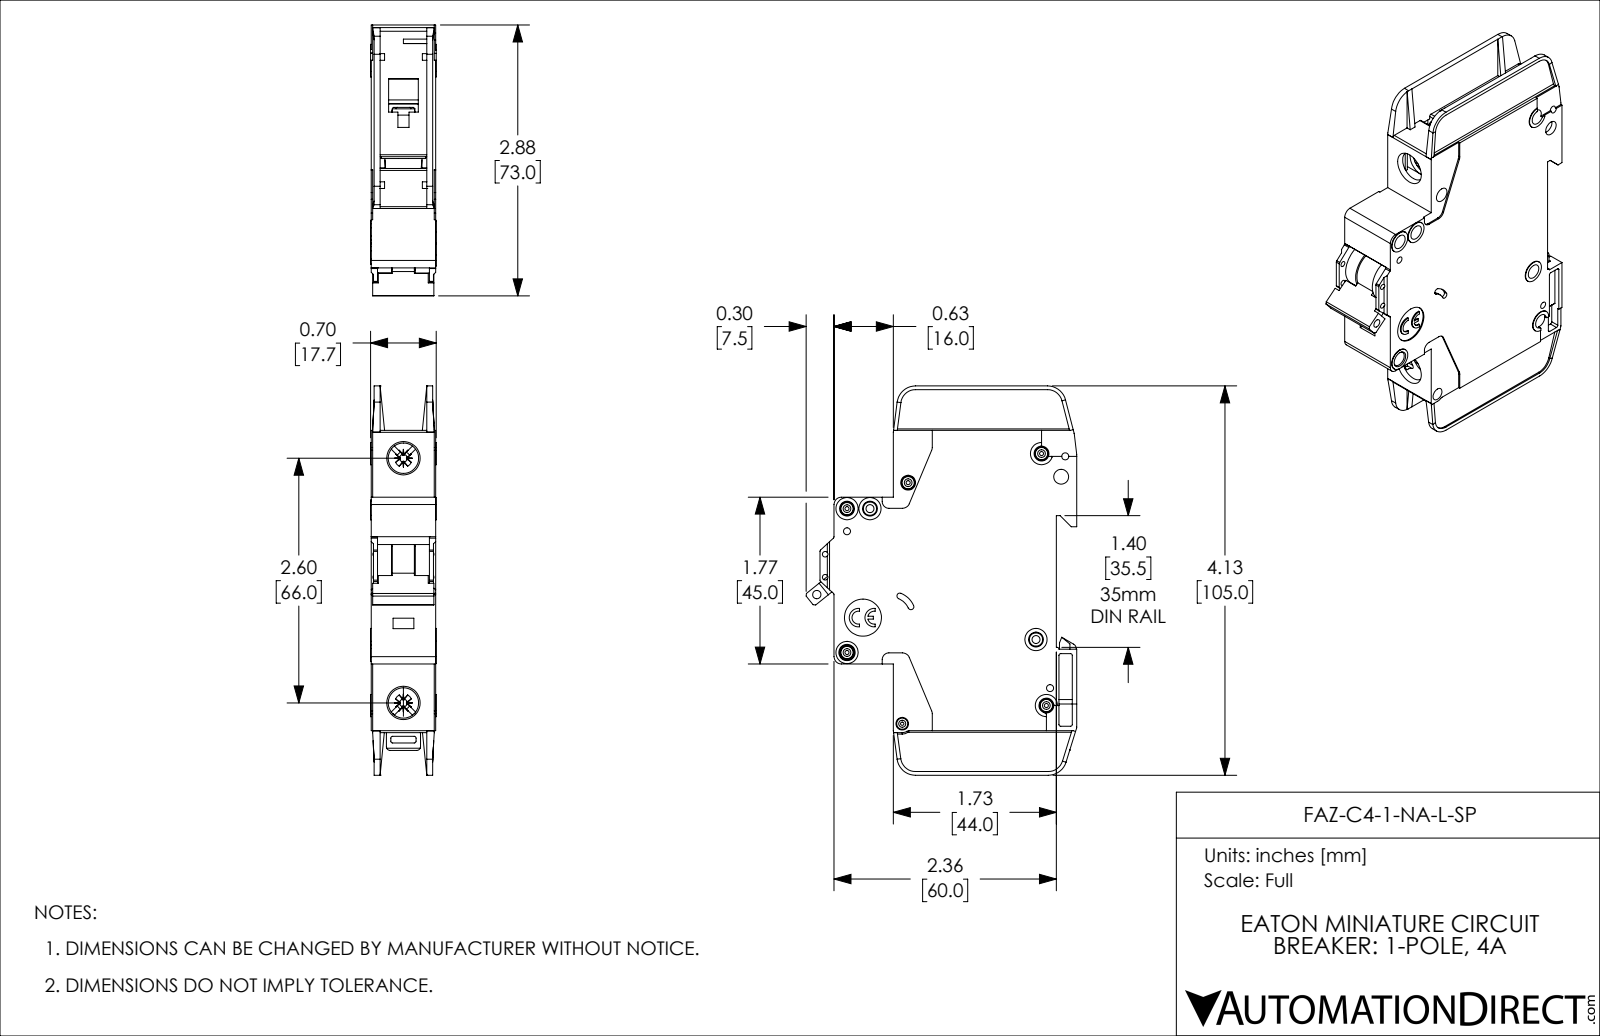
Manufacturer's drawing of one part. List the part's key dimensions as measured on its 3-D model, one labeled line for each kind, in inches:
Part name (STEP PRODUCT): FAZ-C4-1-NA-L-SP
STEP written by: SolidWorks 2019 (AUTOMOTIVE_DESIGN)
Units: inches
Bodies: 1 solid, 1127 faces (671 planar, 357 cylindrical, 99 other)
Overall size (bounding box): 4.134 × 2.876 × 0.697
Volume: 4.682 in³ · Surface area: 41.01 in²
Round holes (diameter × count): ⌀0.157 ×8, ⌀0.043 ×5, ⌀0.075 ×4, ⌀0.059 ×2, ⌀0.085 ×2, ⌀0.323 ×2, ⌀0.035 ×1, ⌀0.089 ×1, ⌀0.098 ×1, ⌀0.134 ×1, ⌀0.394 ×1
Round bosses / shafts (diameter × count): ⌀0.13 ×5, ⌀0.236 ×4, ⌀0.118 ×2, ⌀0.098 ×1
Partial cylindrical surfaces — rounded edges, fillets, slot ends (radius × count): R0.02 ×42, R0.016 ×10, R0.039 ×10, R0.079 ×8, R0.197 ×5, R0.008 ×4, R0.026 ×4, R0.043 ×4
Main face-to-face distances: 0.047, 0.685, 0.591, 0.638, 0.094, 0.543, 0.016, 0.031, 0.496, 0.575
Hole centre spacings: 0.244, 0.537, 0.87, 0.189, 0.199, 0.204, 0.221, 0.24
